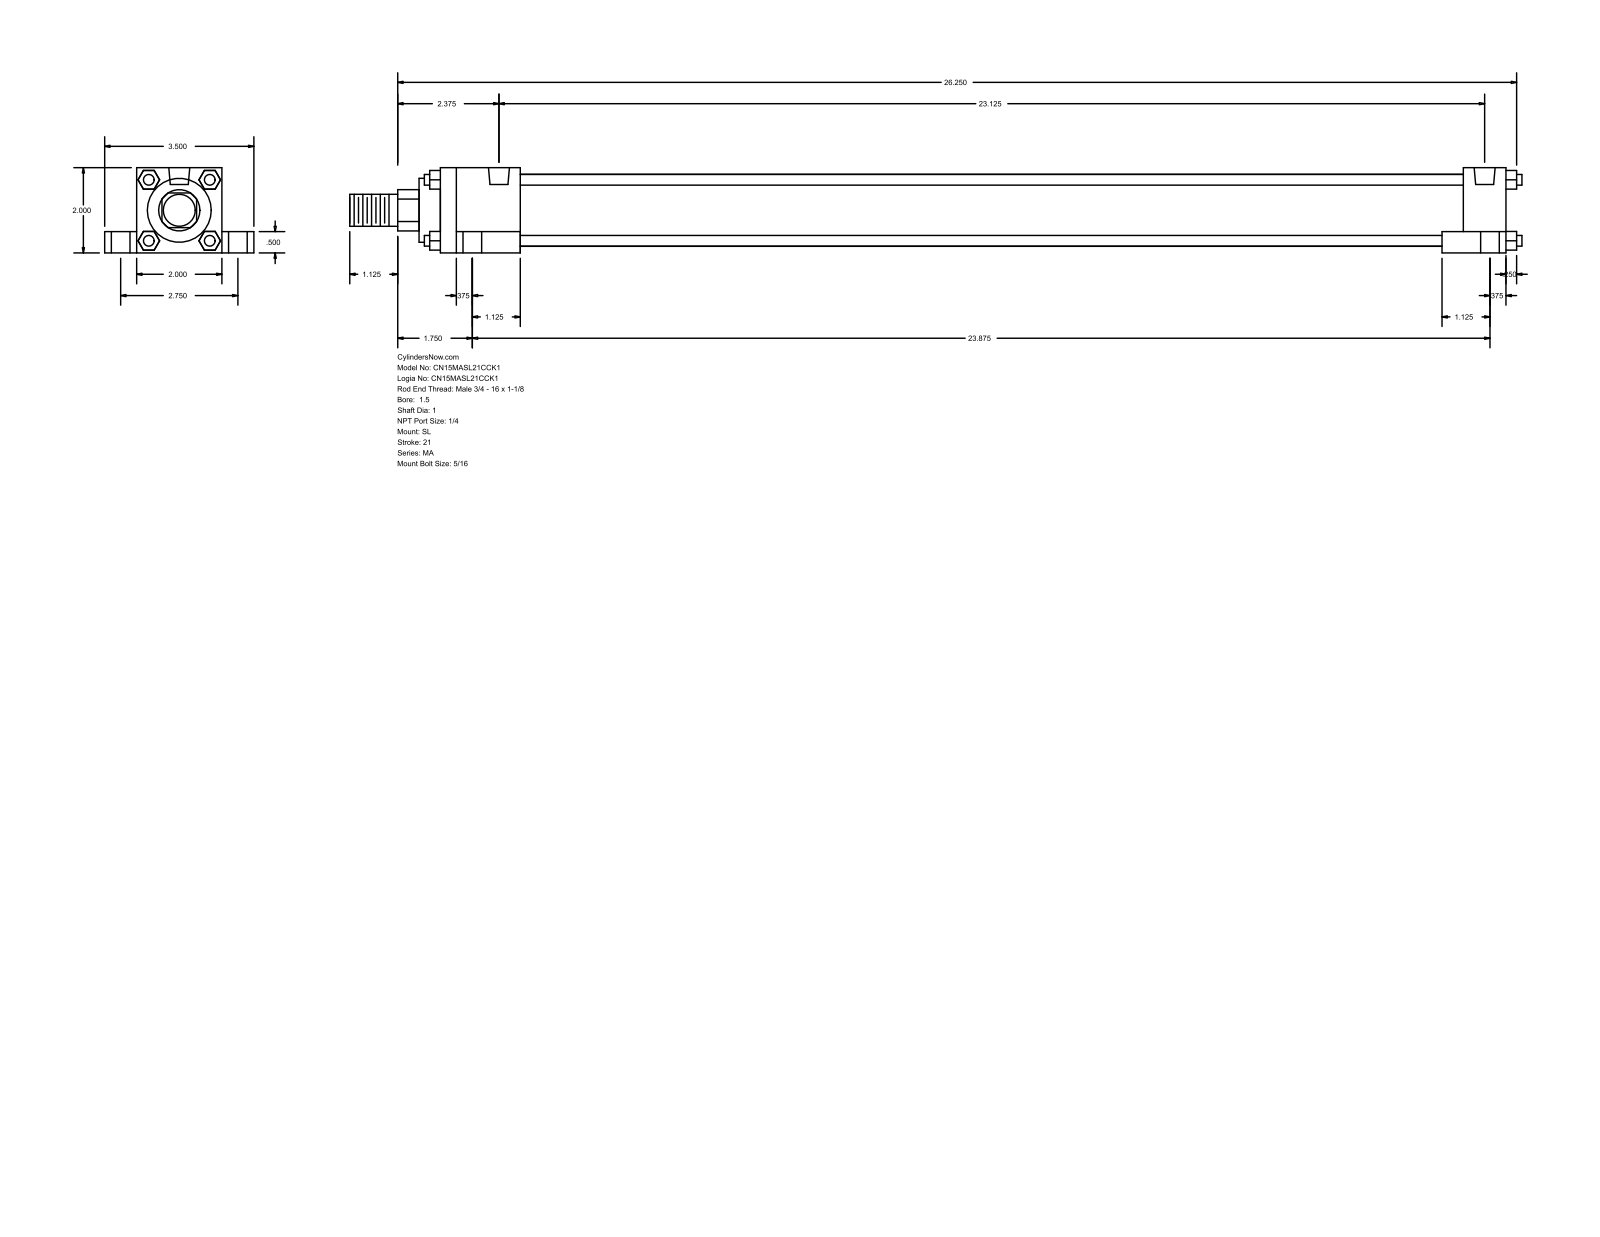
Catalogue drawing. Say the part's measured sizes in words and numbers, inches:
The part is named "MA_SL__0150_1". Its 3-D file was written by "GSSL Pune (CONFIG_CONTROL_DESIGN)". It is 0 solids with 148 faces: 112 planar, 36 cylindrical and 0 other. Overall it measures 27.5 by 3.5 by 2 inches. Round holes: 4 of diameter 0.313, 4 of diameter 0.437, 4 of diameter 0.687, 2 of diameter 0.492. Round bosses or shafts: 4 of diameter 0.25, 1 of diameter 1.69, 1 of diameter 1.5, 1 of diameter 1, 1 of diameter 0.75. Partial cylindrical surfaces (rounded edges, fillets, slot ends): 1 of radius 0.484. The main face-to-face distances are 2, 0.5, 0.75, 2.75, 1.5, 0.375, 25, 1, 0.25, 24. The hole center spacings are 1.38, 1.51, 2.75, 23.125, 23.291, 23.79, 23.875, 24.033.
